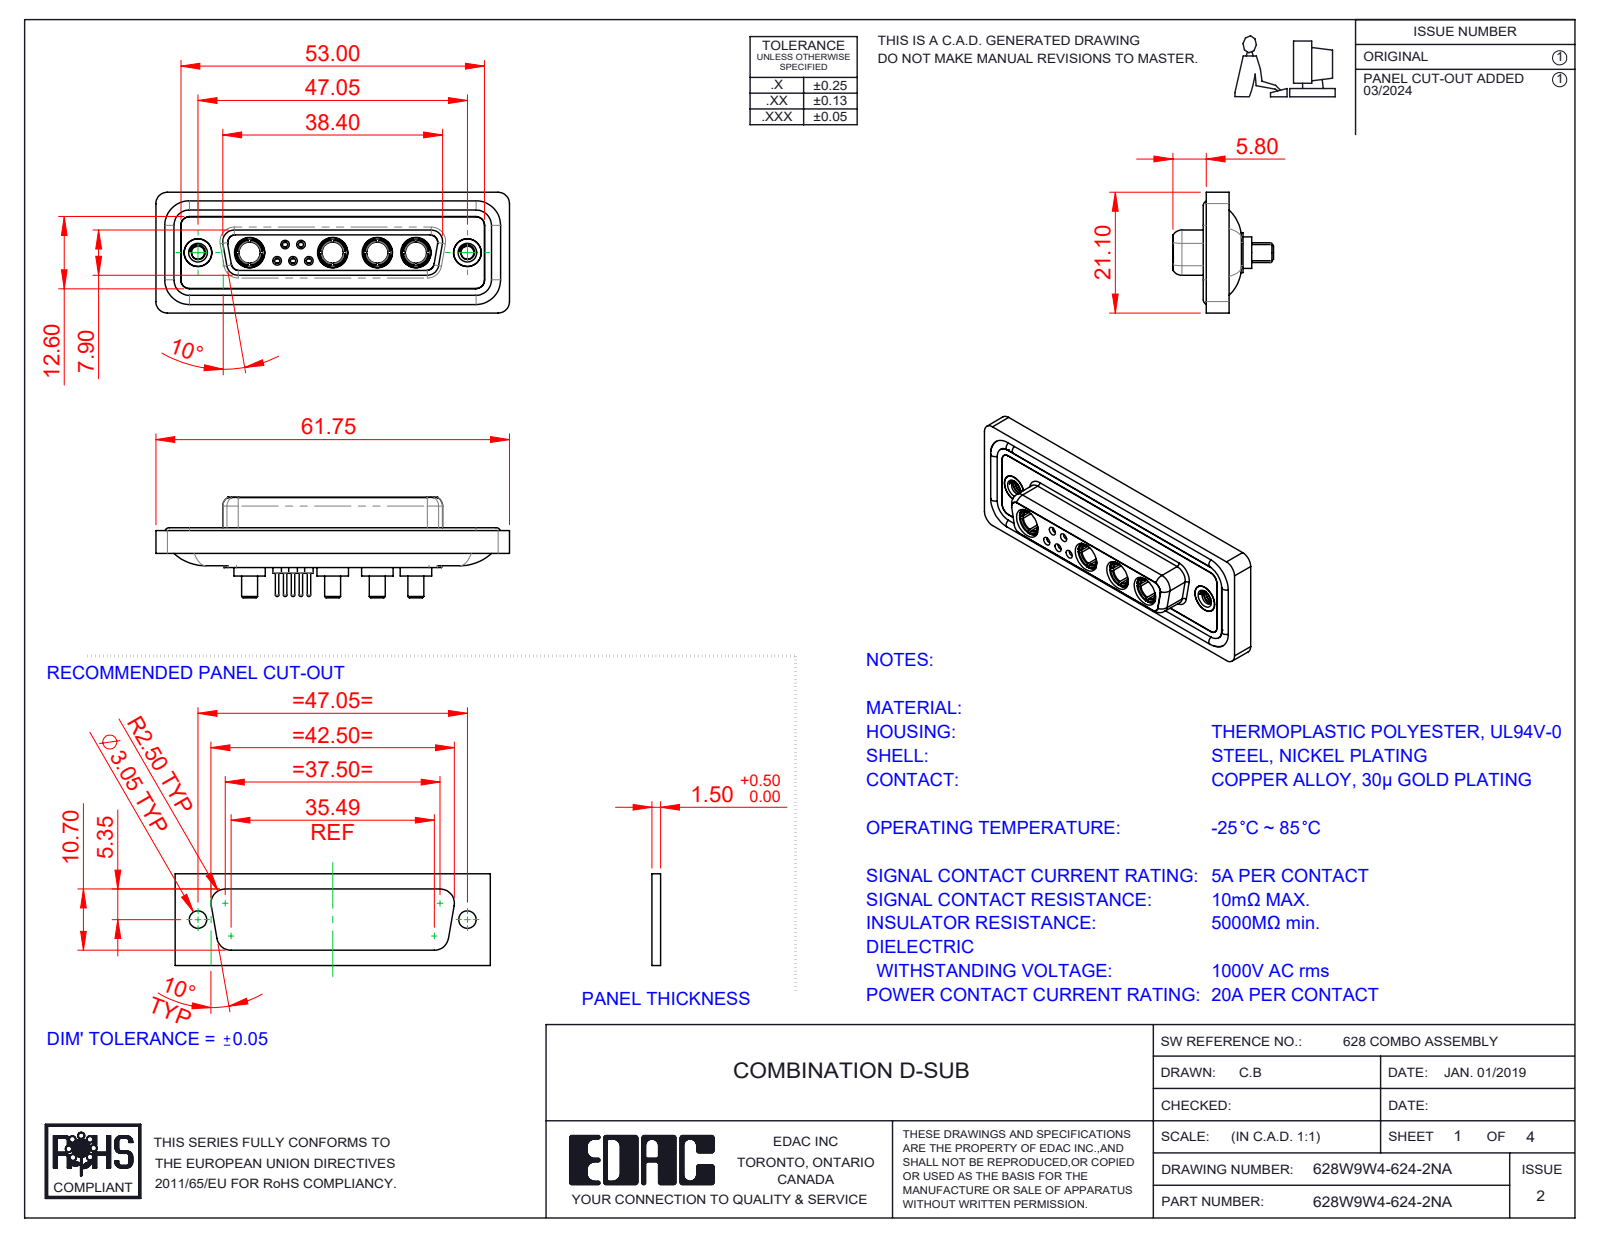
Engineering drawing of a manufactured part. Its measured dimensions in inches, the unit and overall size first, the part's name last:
Units: inches
Overall size (bounding box): 2.431 × 0.831 × 0.691
Round holes (diameter × count): ⌀0.191 ×6, ⌀0.035 ×5, ⌀0.043 ×5, ⌀0.059 ×5, ⌀0.079 ×5, ⌀0.146 ×4, ⌀0.209 ×4, ⌀0.063 ×3, ⌀0.067 ×2, ⌀0.089 ×2, ⌀0.157 ×2, ⌀0.159 ×2
Round bosses / shafts (diameter × count): ⌀0.063 ×6, ⌀0.087 ×5, ⌀0.024 ×5, ⌀0.217 ×4, ⌀0.205 ×4, ⌀0.195 ×4, ⌀0.187 ×4, ⌀0.148 ×4
Partial cylindrical surfaces — rounded edges, fillets, slot ends (radius × count): R0.059 ×22, R0.079 ×18, R0.053 ×8, R0.063 ×8, R0.01 ×4, R0.02 ×4, R0.024 ×4, R0.026 ×4
Main face-to-face distances: 0.016, 0.071, 0.293, 0.222, 0.02, 0.278, 0.26, 0.063, 0.043, 0.114
Hole centre spacings: 0.124, 0.109, 0.198, 0.109, 0.173, 0.198, 0.218, 0.226
Volume: 0.502 in³ · Surface area: 21.02 in²
Bodies: 20 solids, 955 faces (296 planar, 377 cylindrical, 282 other)
Part name (STEP PRODUCT): 628Combo Contact Row 1_24; 628Combo Threaded Rivet_A; 628W9W4-624-2NA; 628Combo Contact Row 2_24 (+5 more)
STEP written by: SolidWorks 2023 (CONFIG_CONTROL_DESIGN)
